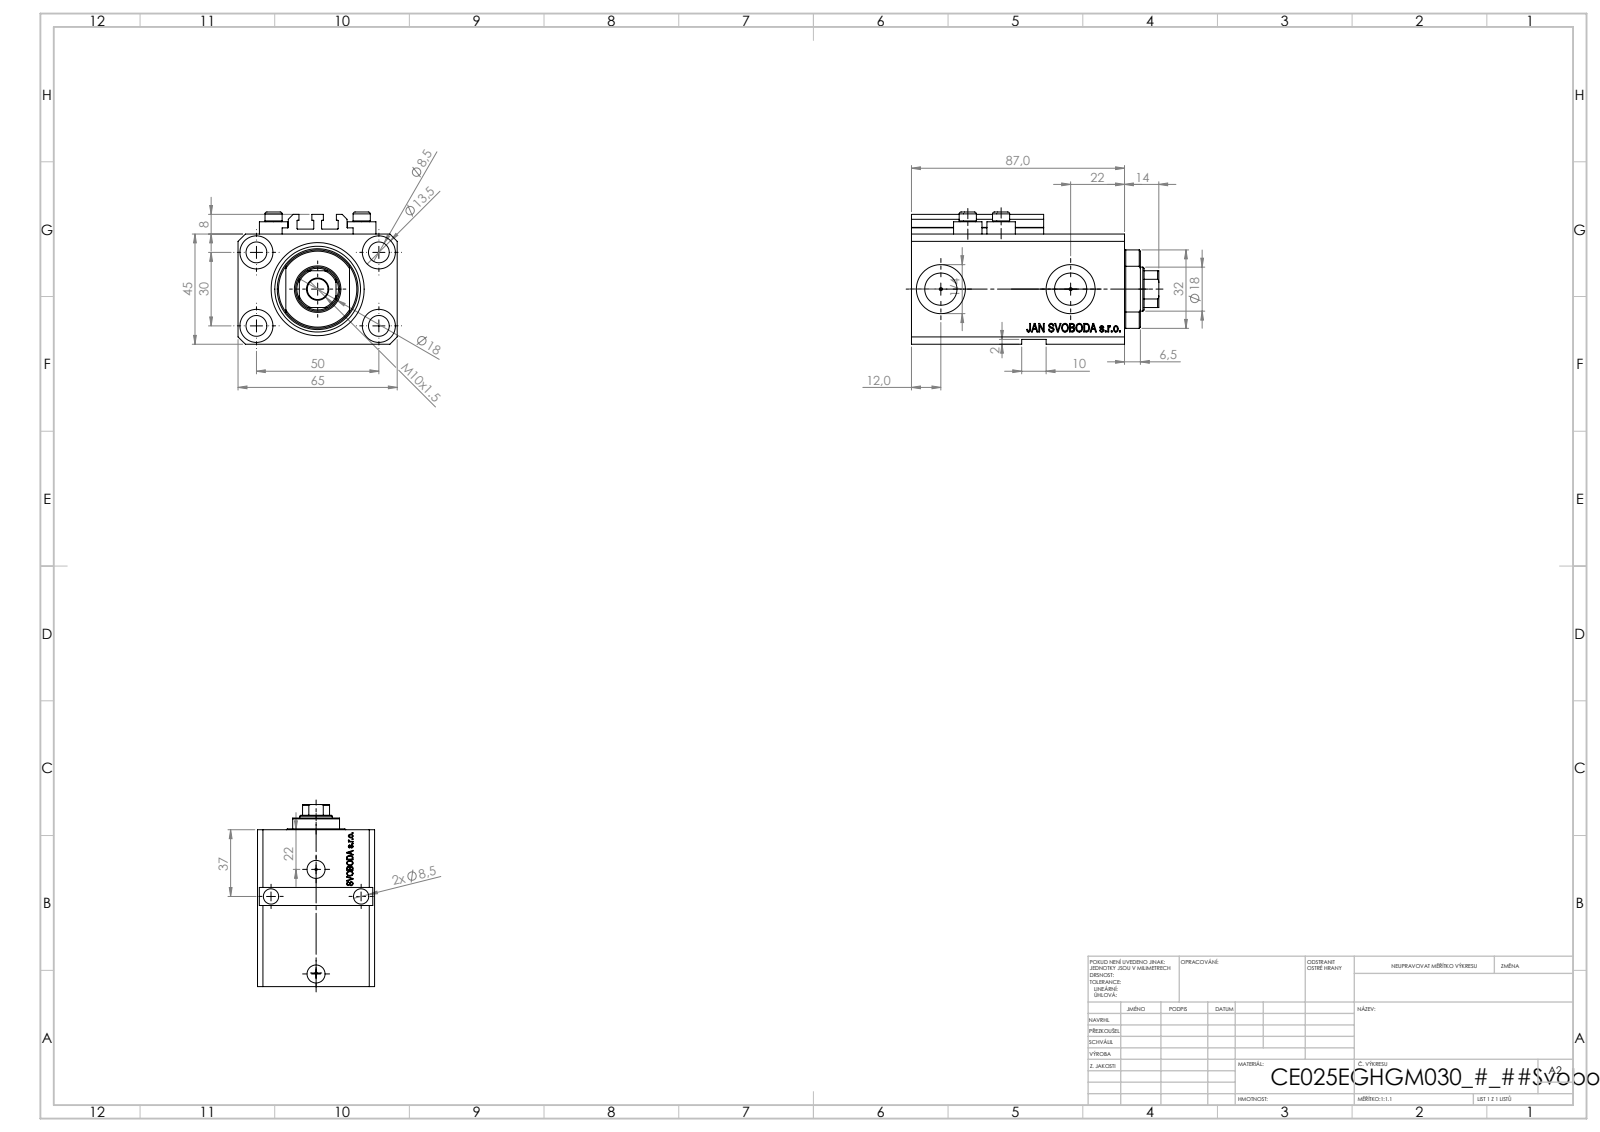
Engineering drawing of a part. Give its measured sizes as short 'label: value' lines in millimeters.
name: ALLEN BOLT V250CE; V250CE_VC_E; V250CE_E_Body; V250CE_C_VCP
written by: SolidWorks 2019 (CONFIG_CONTROL_DESIGN)
unit: mm
bodies: 8 solids, 1067 faces (511 planar, 126 cylindrical, 430 other)
size: 101 × 65 × 54
volume: 225 473 mm³; area: 64 742 mm²
holes: 7× ⌀8.5, 4× ⌀1.25, 4× ⌀4, 4× ⌀13.5, 2× ⌀10, 2× ⌀13.16, 2× ⌀20, 1× ⌀18, 1× ⌀25, 1× ⌀38
bosses: 4× ⌀11.6, 4× ⌀7
rounds: 10× R0.2, 1× R8.5, 1× R16
face distances: 45, 65, 73, 14, 2, 87, 47, 6.9, 66.1, 80.1
hole spacings: 29.15, 50, 13.6, 15.12, 23.73, 24.08, 27.89, 30
